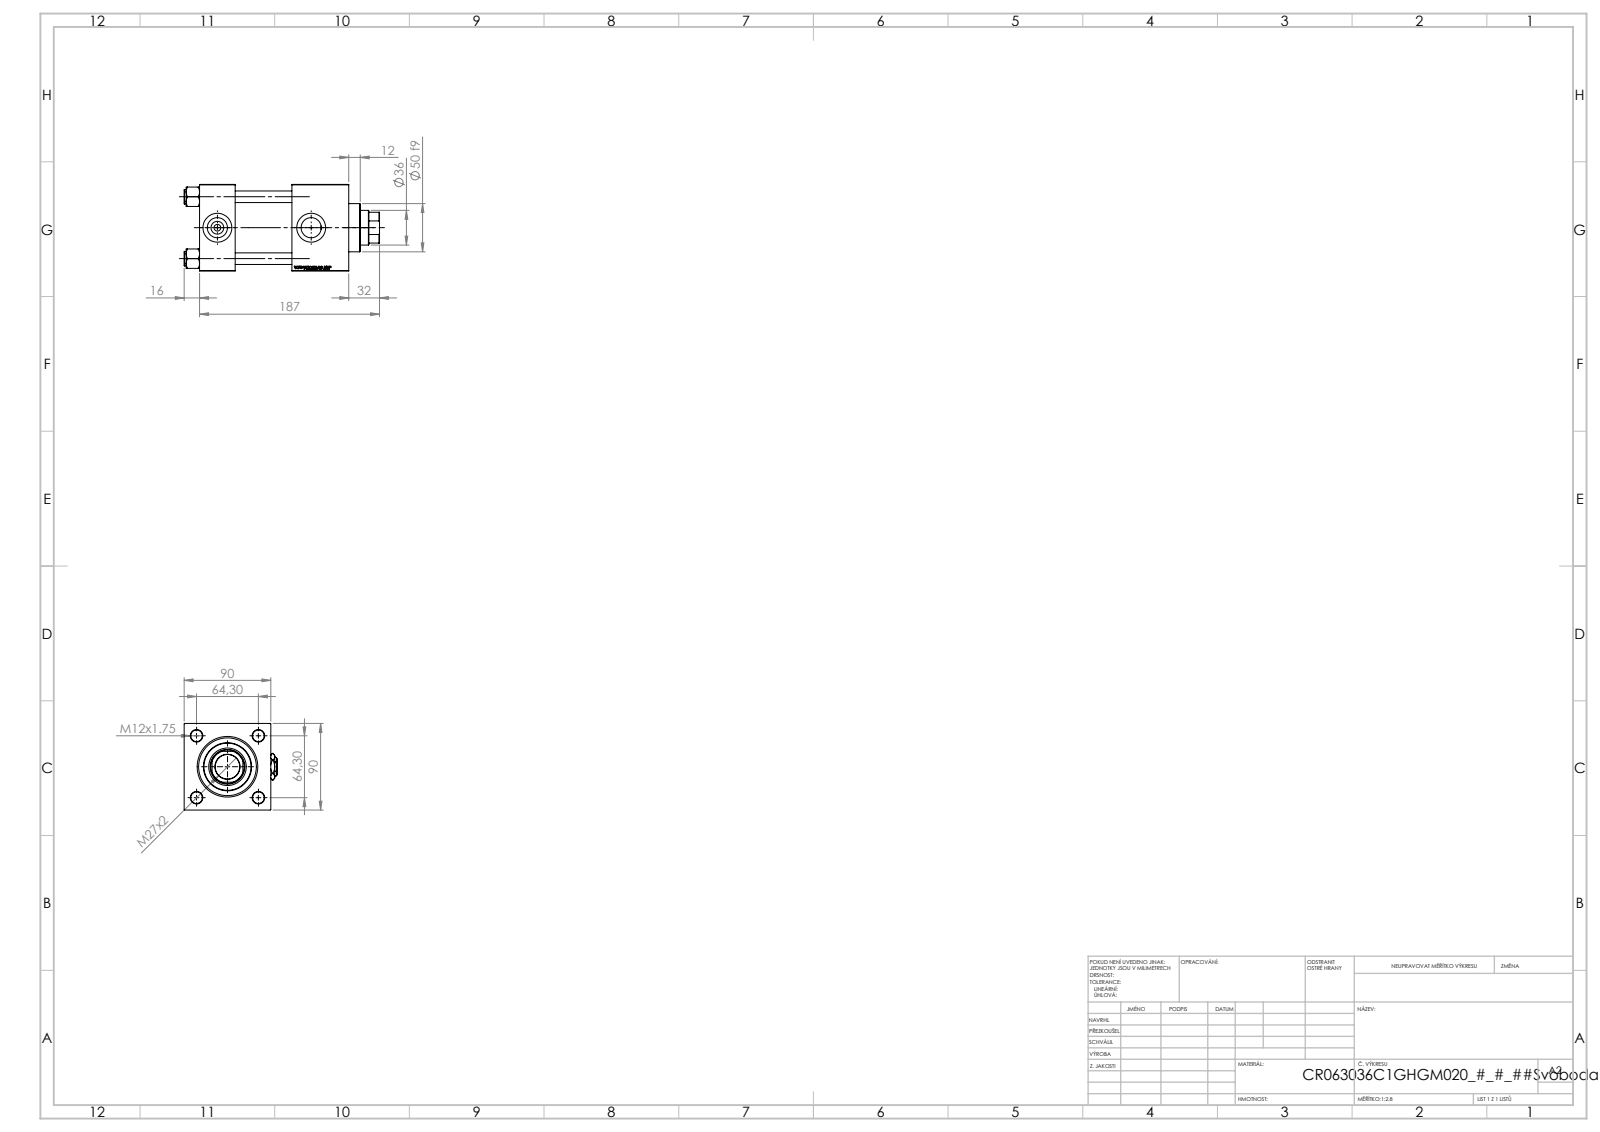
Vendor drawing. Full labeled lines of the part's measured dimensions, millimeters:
Part name (STEP PRODUCT): V215CR_C_TYCINKA; NUT_M5_C; V215CR_C_Body; V215CR_VCP_C (+2 more)
STEP written by: SolidWorks 2019 (CONFIG_CONTROL_DESIGN)
Units: millimetres
Bodies: 12 solids, 1196 faces (550 planar, 90 cylindrical, 556 other)
Overall size (bounding box): 203 × 97 × 90
Volume: 963 527 mm³ · Surface area: 186 357 mm²
Round holes (diameter × count): ⌀12 ×4, ⌀7 ×2, ⌀20.96 ×2, ⌀30 ×2, ⌀25.5 ×1, ⌀36 ×1, ⌀39 ×1, ⌀50 ×1, ⌀60 ×1, ⌀63 ×1
Round bosses / shafts (diameter × count): ⌀15 ×4, ⌀69 ×1
Partial cylindrical surfaces — rounded edges, fillets, slot ends (radius × count): R17.5 ×1
Main face-to-face distances: 90, 59, 37, 118, 155, 96, 126.3, 89.3, 30.3, 28.7
Hole centre spacings: 45.47, 64.3, 90.93, 97.5
